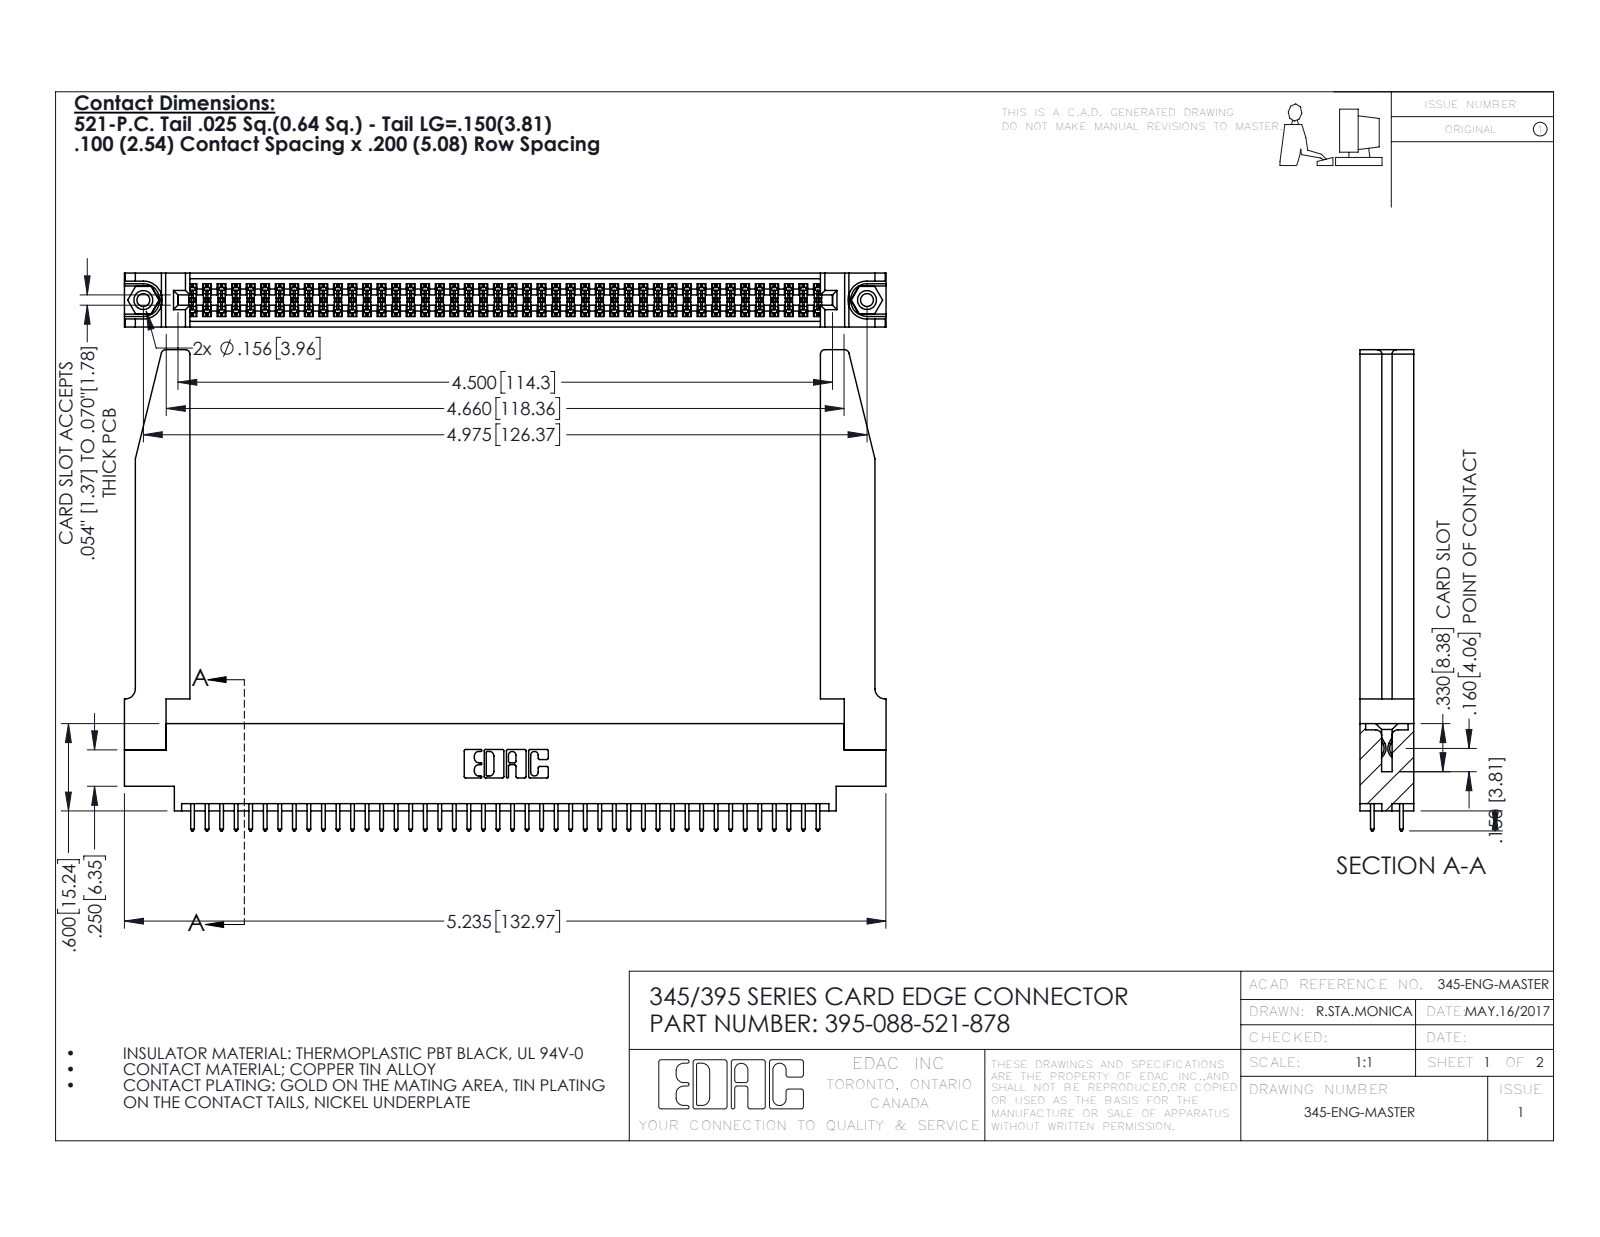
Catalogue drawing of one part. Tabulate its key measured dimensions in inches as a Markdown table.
| quantity | value |
| --- | --- |
| part name | 345-250-001_345-250-001-102; 345-220-078_345-220-078; 395-088-521-878; 345-292-001_345-293-121 (+1 more) |
| STEP written by | SolidWorks 2016 (CONFIG_CONTROL_DESIGN) |
| units | inches |
| bodies | 93 solids, 4764 faces (3130 planar, 1582 cylindrical, 52 other) |
| overall size | 5.236 × 3.307 × 0.37 |
| volume | 1.255 in³ |
| surface area | 39.82 in² |
| round holes (diameter × count) | 0.089 × 2, 0.125 × 2, 0.156 × 2, 0.064 × 1 |
| round bosses / shafts (diameter × count) | 0.155 × 2 |
| partial cylindrical surfaces (radius × count) | 0.006 × 132, 0.01 × 88, 0.01 × 22, 0.03 × 8, 0.007 × 6, 0.031 × 6, 0.026 × 3, 0.014 × 2 |
| main face-to-face distances | 0.37, 0.072, 0.298, 0.2, 0.098, 0.272, 0.025, 0.225, 0.175, 0.148 |
| hole center spacings | 0.27, 4.739, 4.975 |
